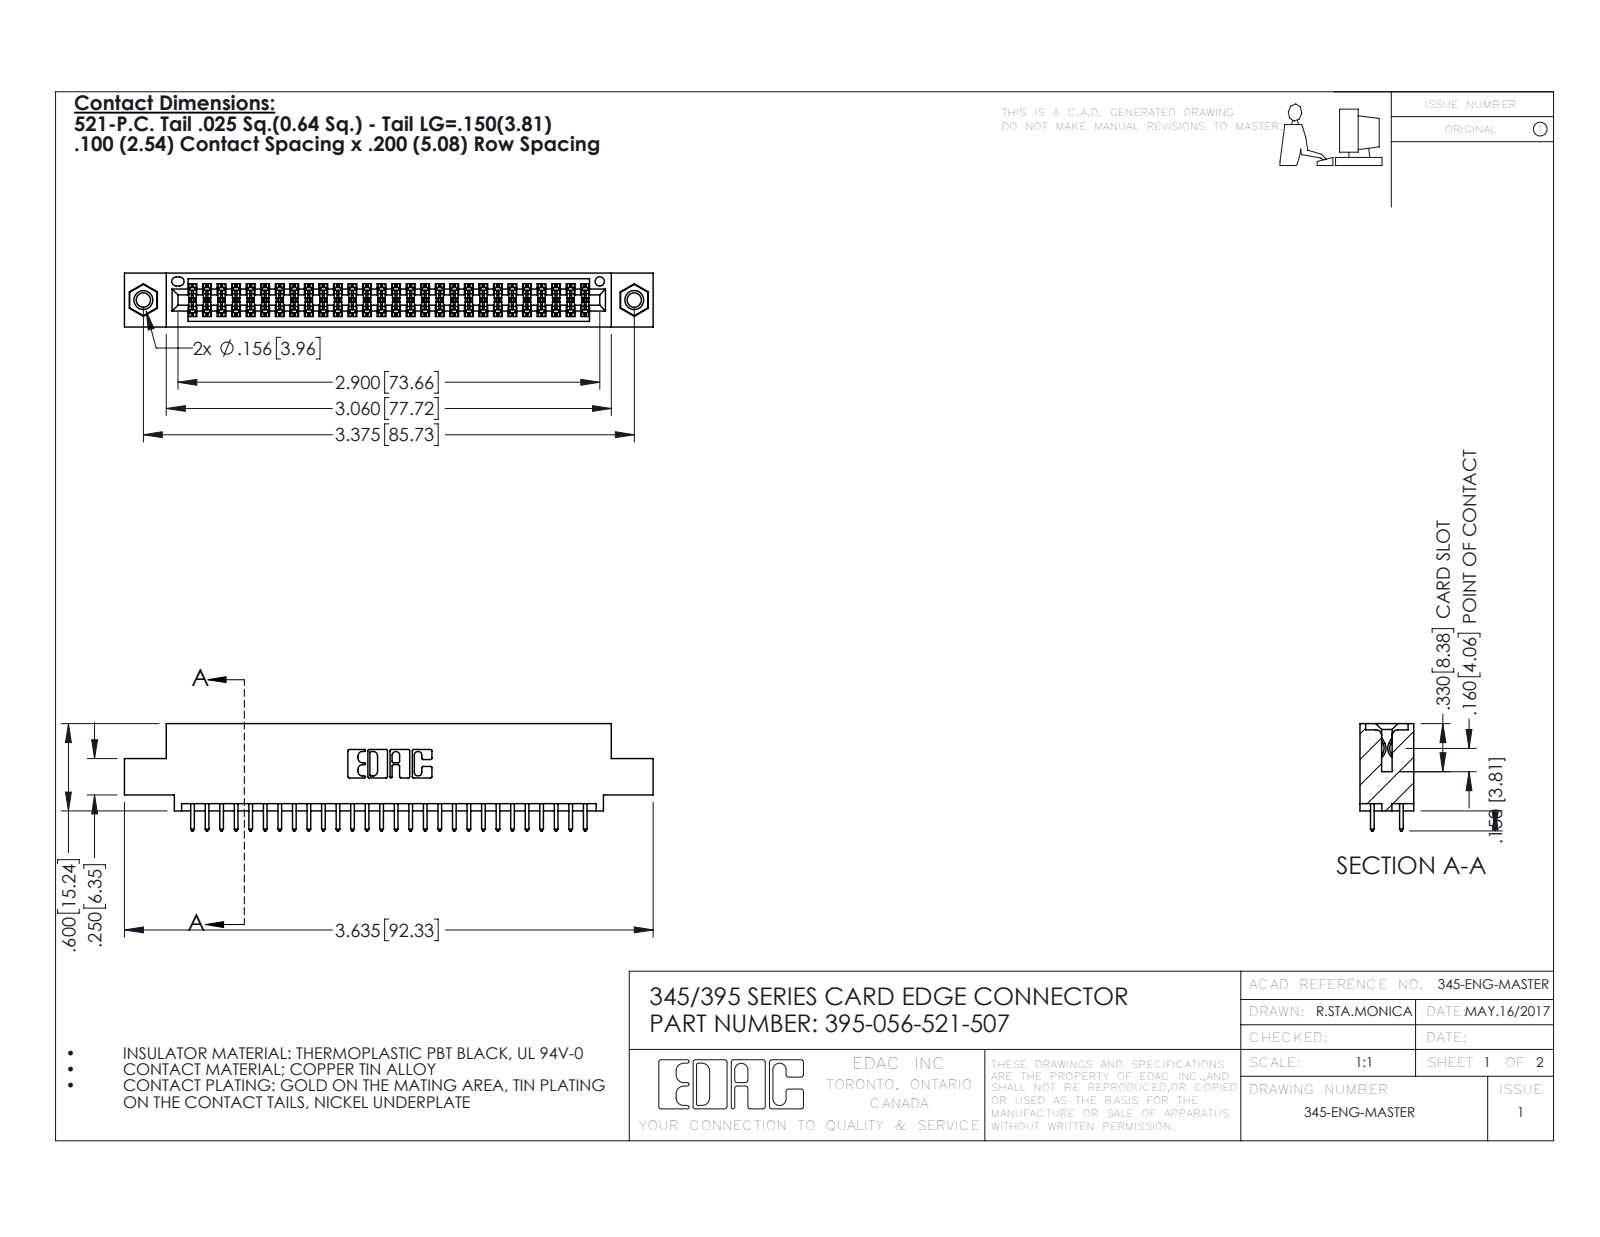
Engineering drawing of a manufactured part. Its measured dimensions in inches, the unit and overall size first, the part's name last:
Units: inches
Overall size (bounding box): 3.635 × 0.737 × 0.37
Round holes (diameter × count): ⌀0.098 ×2, ⌀0.125 ×2, ⌀0.156 ×2, ⌀0.064 ×1
Round bosses / shafts (diameter × count): ⌀0.155 ×2
Partial cylindrical surfaces — rounded edges, fillets, slot ends (radius × count): R0.006 ×84, R0.01 ×56, R0.01 ×22, R0.007 ×6, R0.031 ×6, R0.026 ×3, R0.014 ×2, R0.019 ×2
Main face-to-face distances: 0.072, 0.298, 0.2, 0.37, 0.098, 0.272, 0.025, 0.225, 0.175, 0.149
Hole centre spacings: 0.27, 3.14, 3.375
Volume: 0.533 in³ · Surface area: 19.54 in²
Bodies: 59 solids, 2990 faces (1964 planar, 1010 cylindrical, 16 other)
Part name (STEP PRODUCT): 395-056-521-507; 345 Part_0.110 Offset - 0.156 Dia-TI; 345-250-001_345-250-005-103; 345-292-001_345-293-121
STEP written by: SolidWorks 2016 (CONFIG_CONTROL_DESIGN)
